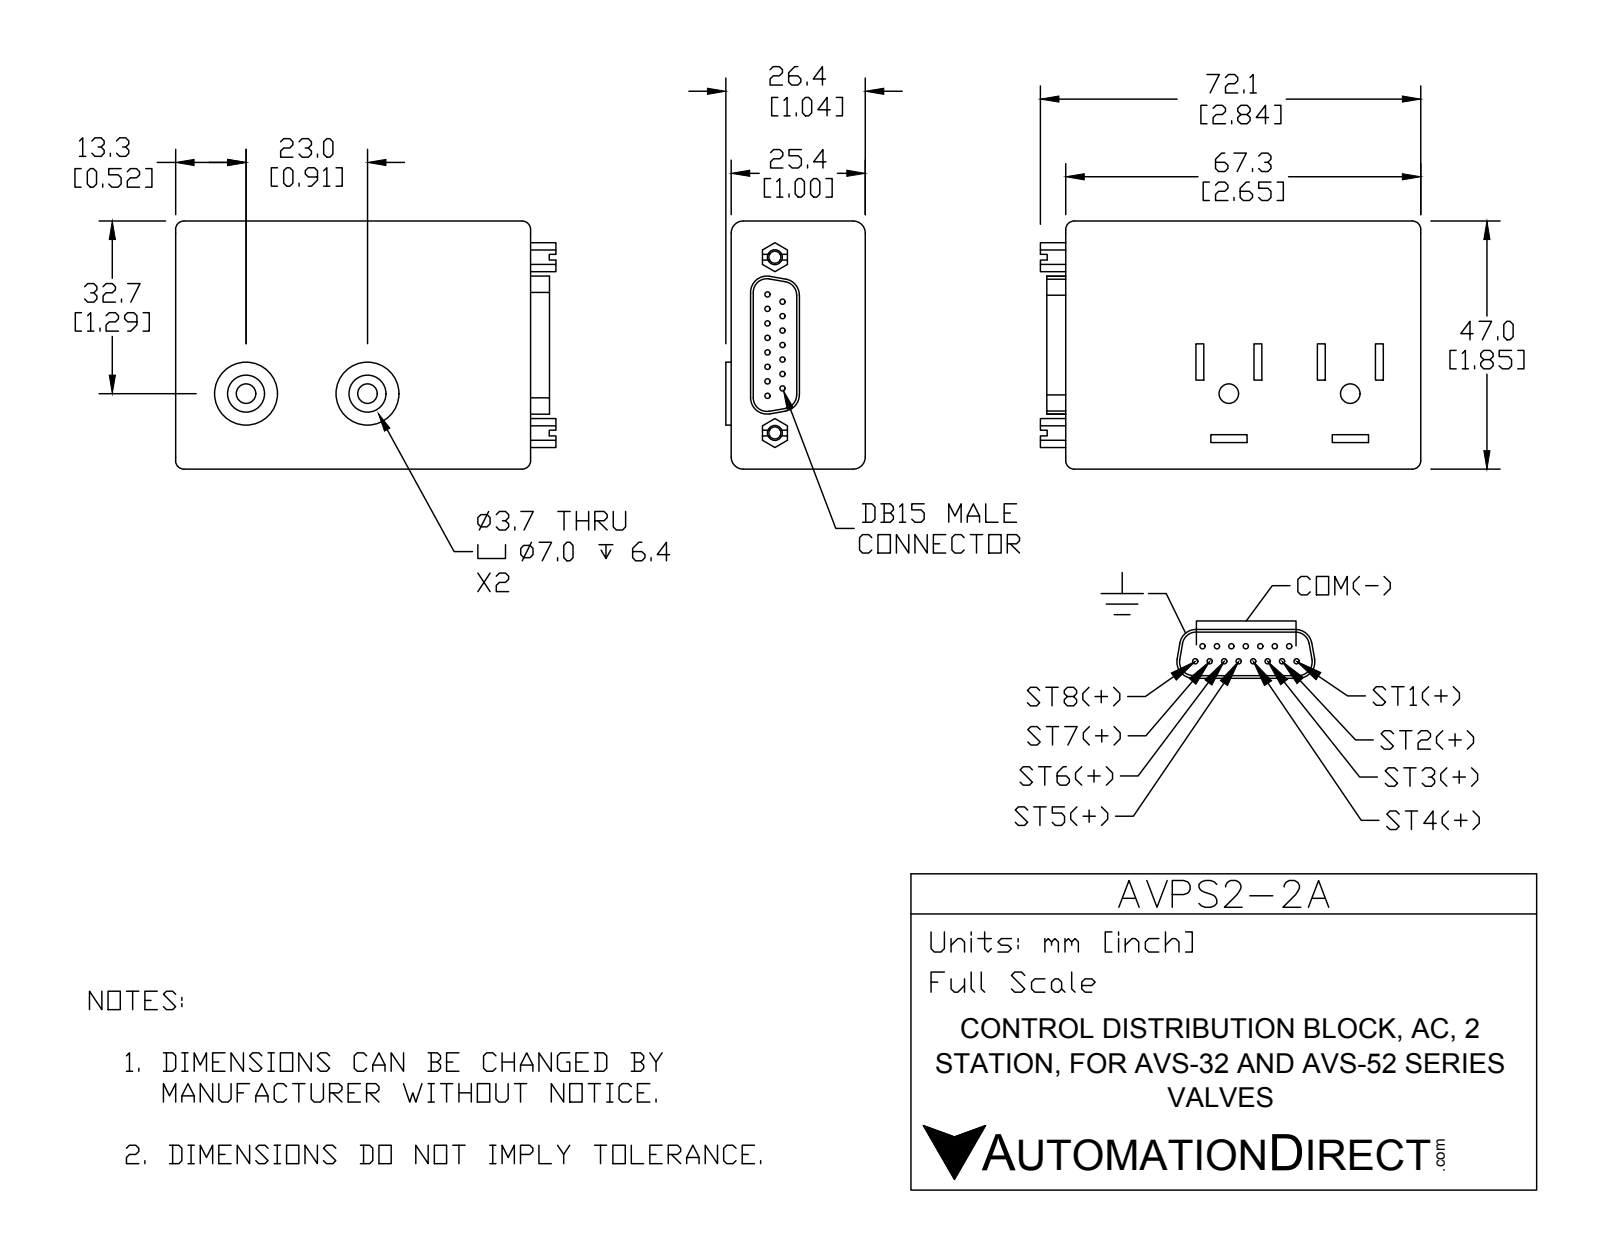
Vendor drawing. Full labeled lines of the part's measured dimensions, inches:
Part name (STEP PRODUCT): AVPS2-2A
STEP written by: SolidWorks 2016 (AUTOMOTIVE_DESIGN)
Units: inches
Bodies: 1 solid, 173 faces (93 planar, 68 cylindrical, 12 other)
Overall size (bounding box): 2.837 × 1.85 × 1.04
Volume: 4.788 in³ · Surface area: 22.01 in²
Round holes (diameter × count): ⌀0.089 ×2, ⌀0.145 ×2, ⌀0.275 ×2
Round bosses / shafts (diameter × count): ⌀0.039 ×15, ⌀0.469 ×2
Partial cylindrical surfaces — rounded edges, fillets, slot ends (radius × count): R0.062 ×6, R0.09 ×4, R0.102 ×4, R0.122 ×4, R0.063 ×2
Main face-to-face distances: 1, 1.85, 2.648, 0.059, 0.123, 2.525, 0.906, 0.433, 0.02, 0.04
Hole centre spacings: 0.906, 1.311
